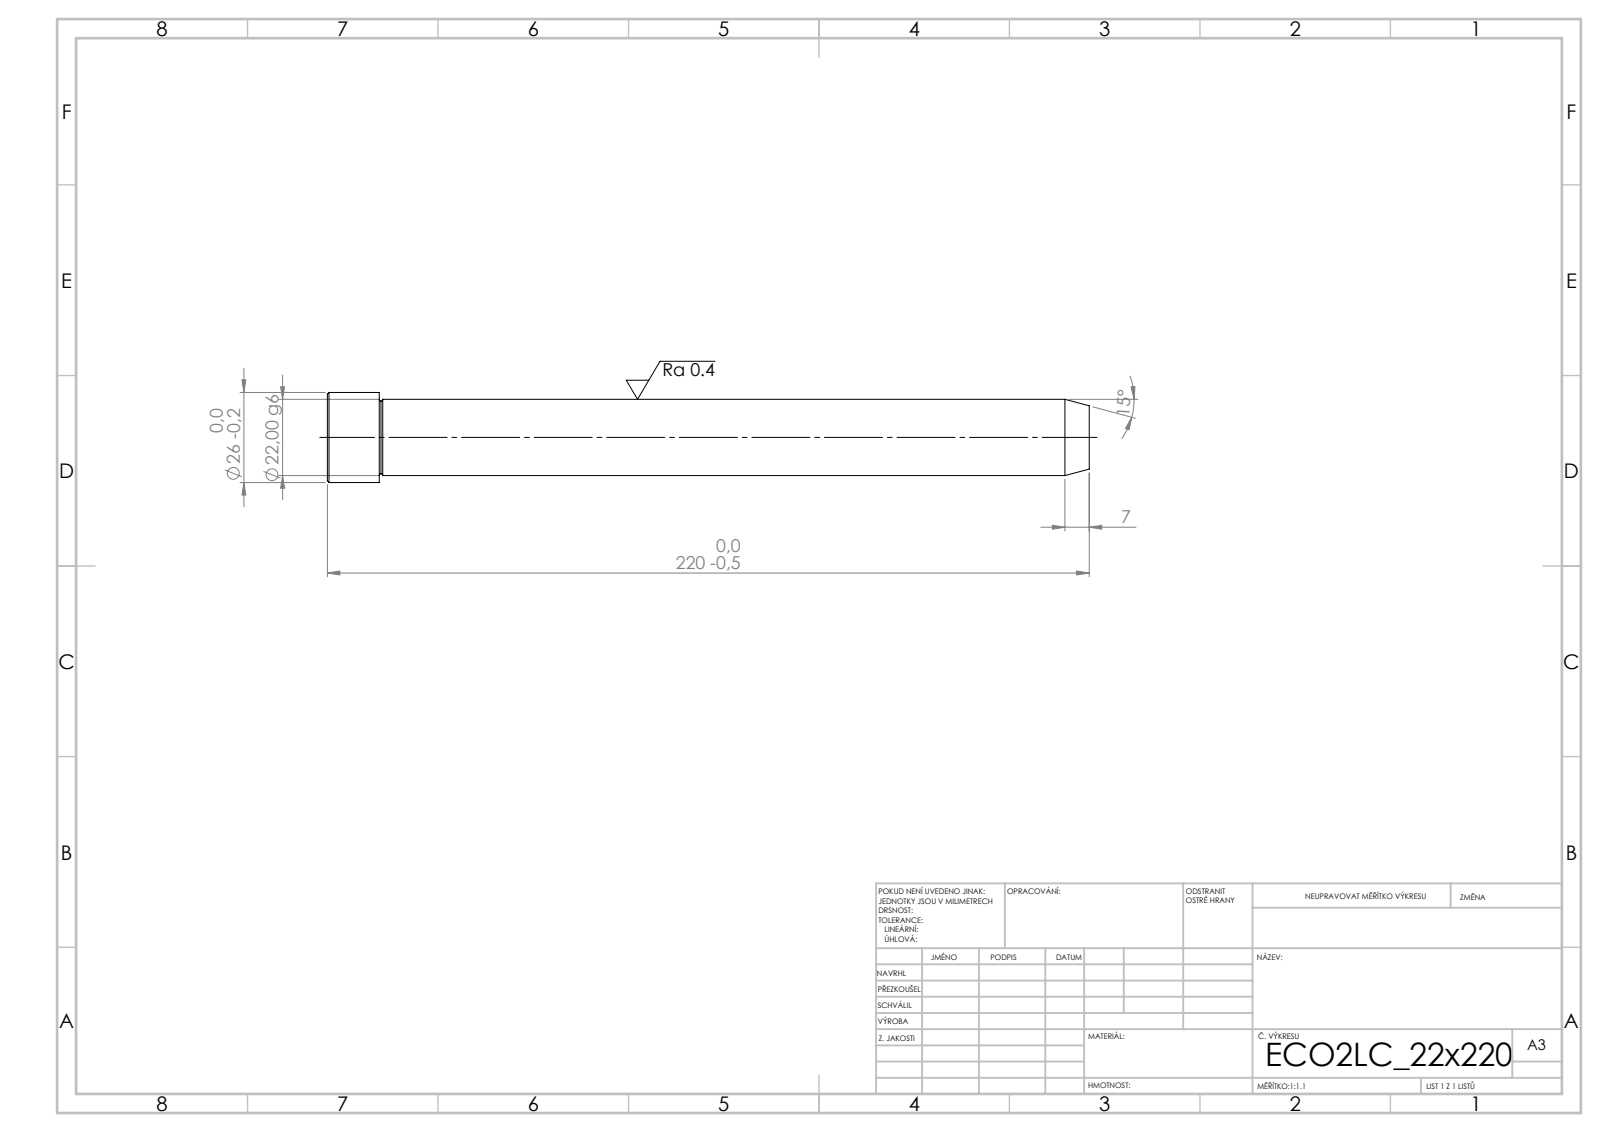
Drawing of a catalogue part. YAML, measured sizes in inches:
step_written_by: "SolidWorks 2019 (CONFIG_CONTROL_DESIGN)"
units: inches
bodies: {solids: 1, faces: 15, planar: 3, cylindrical: 4, other: 8}
overall_size: [8.661, 1.024, 1.024]
volume: 5.213
surface_area: 25.3
round_bosses_or_shafts:
  - {diameter: 1.024, count: 1}
  - {diameter: 0.866, count: 1}
face_to_face_distances: [8.661, 8.071, 0.591]
